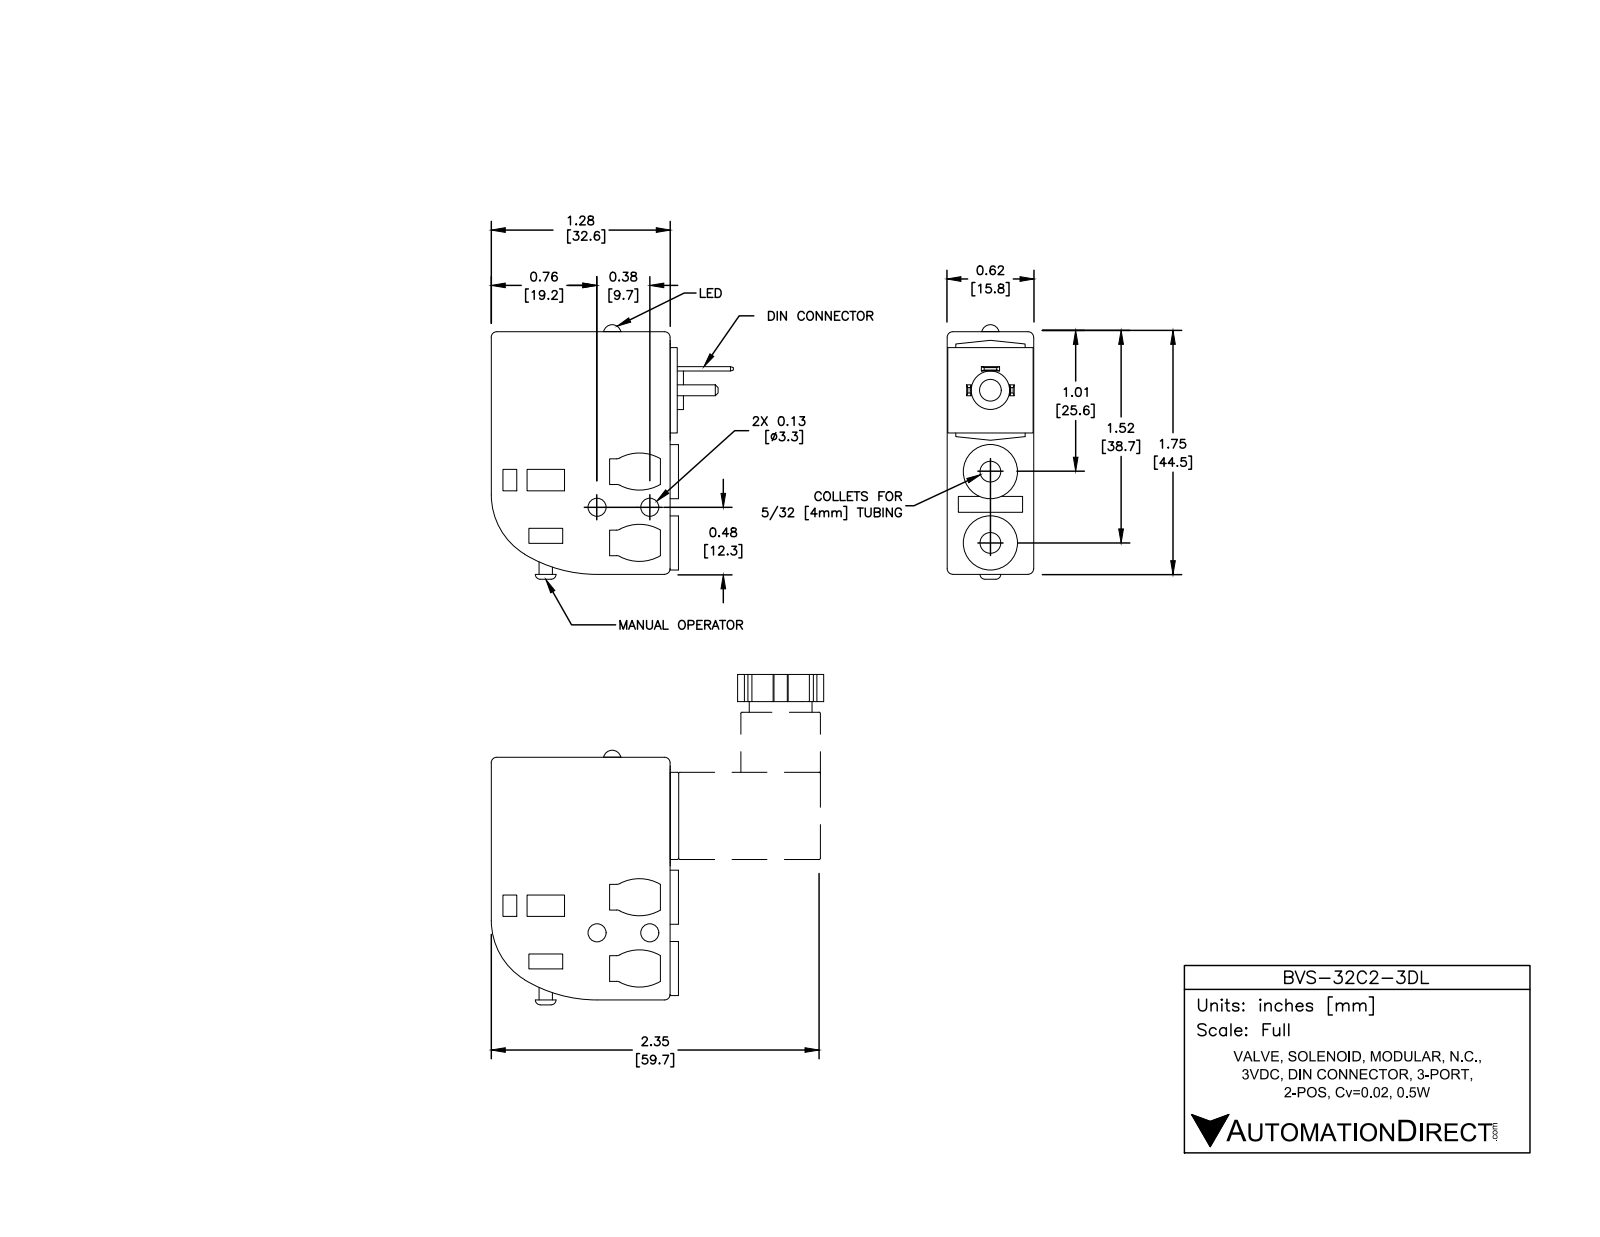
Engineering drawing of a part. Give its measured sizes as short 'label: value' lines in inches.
name: BVS-32C2-3DL
written by: SolidWorks 2016 (AUTOMOTIVE_DESIGN)
unit: in
bodies: 1 solid, 162 faces (112 planar, 46 cylindrical, 4 other)
size: 1.84 × 1.75 × 0.62
volume: 1.279 in³; area: 10.75 in²
holes: 2× ⌀0.13, 2× ⌀0.15, 2× ⌀0.25, 1× ⌀0.05, 1× ⌀0.16
bosses: 2× ⌀0.39, 1× ⌀0.28, 1× ⌀0.1
rounds: 4× R0.05, 4× R0.3, 3× R0.04, 1× R0.5, 1× R1
face distances: 0.62, 0.1, 1.29, 0.52, 1.341, 0.051, 1.75, 1, 0.15, 0.06
hole spacings: 0.06, 0.38, 0.45, 0.51, 0.59, 0.65, 1.1
